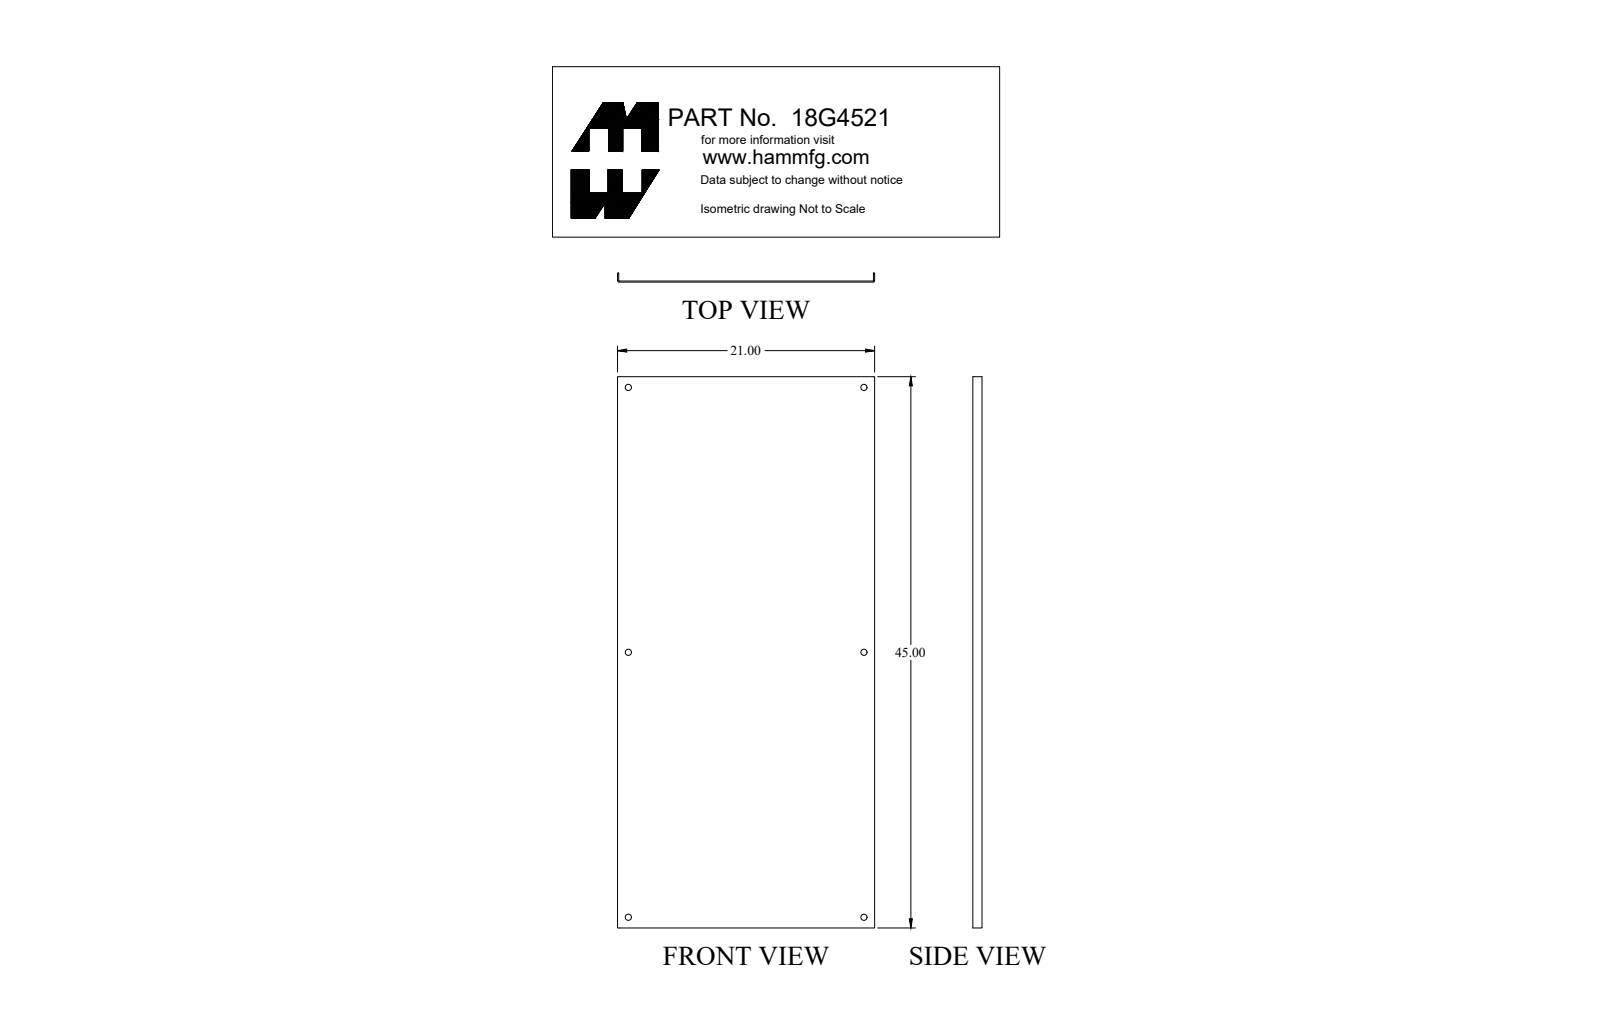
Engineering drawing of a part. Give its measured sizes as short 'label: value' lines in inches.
name: 18G4521_Default
written by: SolidWorks 2018 (CONFIG_CONTROL_DESIGN)
unit: in
bodies: 1 solid, 26 faces (10 planar, 16 cylindrical, 0 other)
size: 45 × 21 × 0.75
volume: 94.98 in³; area: 2 013 in²
holes: 6× ⌀0.5
rounds: 2× R0.03, 2× R0.125
face distances: 0.095, 20.905, 20.81, 21, 0.75, 0.655, 45
hole spacings: 21.625, 28.951, 19.25, 43.25, 47.34
